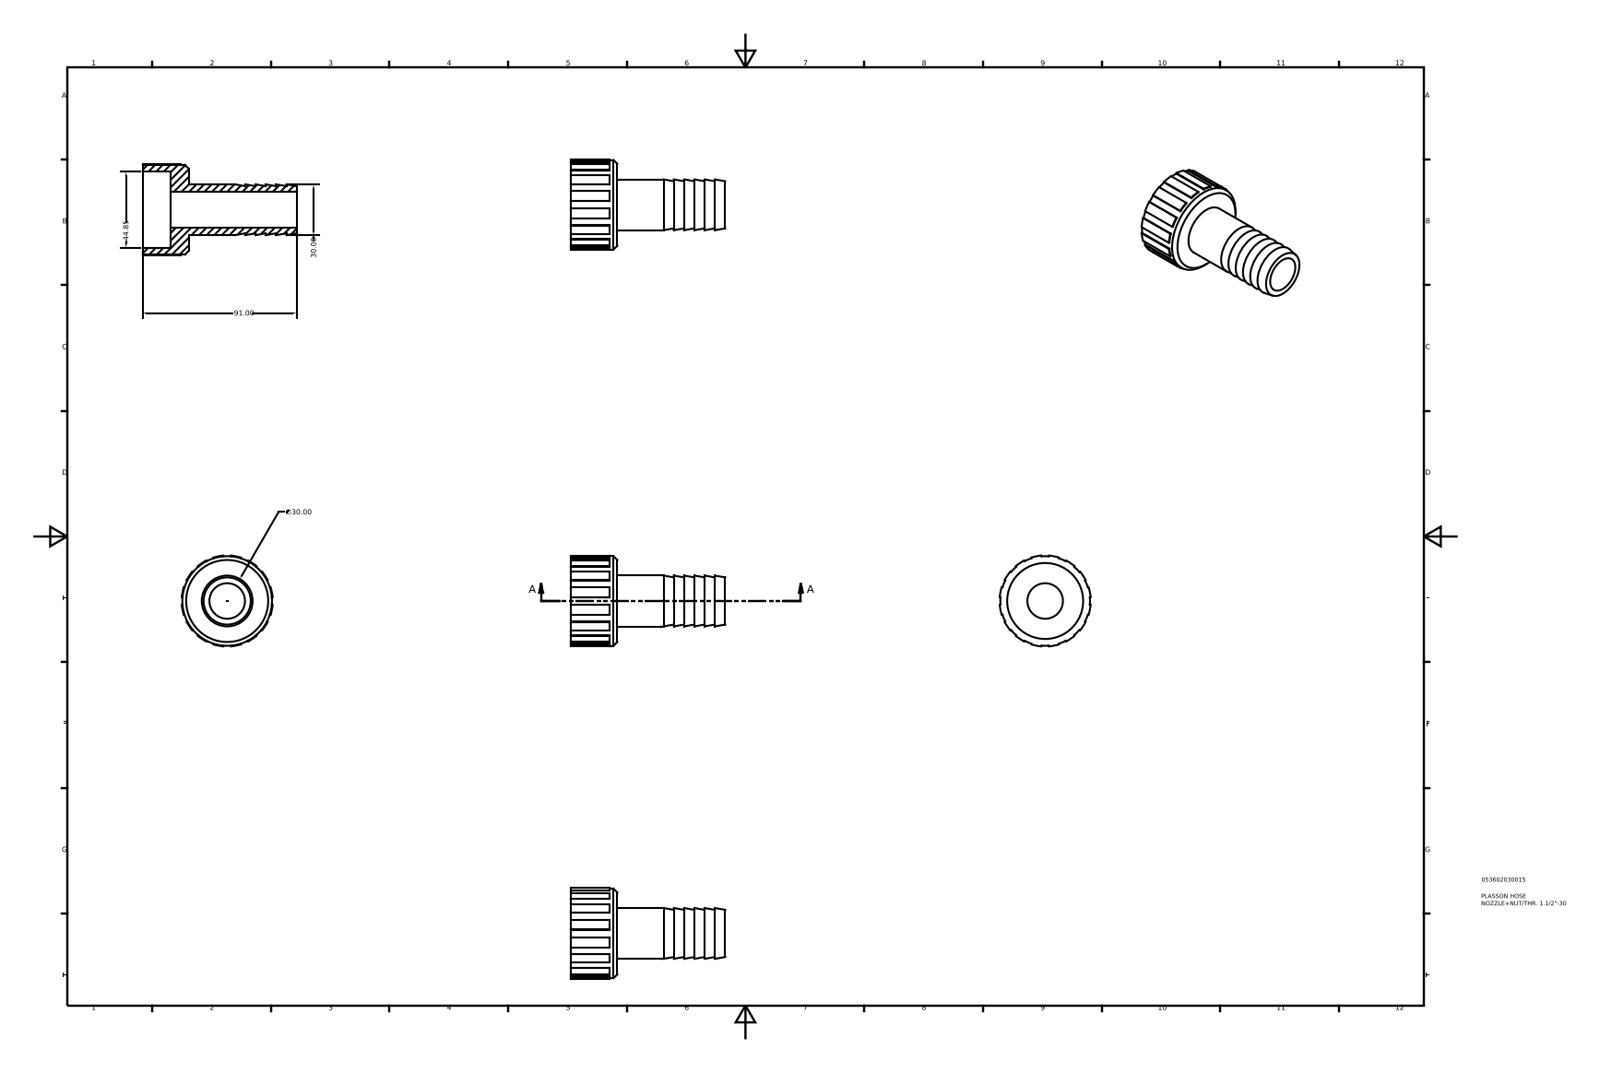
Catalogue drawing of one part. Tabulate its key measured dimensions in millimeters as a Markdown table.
| quantity | value |
| --- | --- |
| part name | 053602030015 |
| STEP written by | Autodesk Inventor 2015 (AUTOMOTIVE_DESIGN) |
| units | millimeters |
| bodies | 1 solid, 84 faces (57 planar, 20 cylindrical, 7 other) |
| overall size | 91 × 53.63 × 53.63 |
| volume | 52 136 mm³ |
| surface area | 22 021 mm² |
| round holes (diameter × count) | 21 × 1, 44.84 × 1 |
| round bosses / shafts (diameter × count) | 52.92 × 1, 30 × 1 |
| partial cylindrical surfaces (radius × count) | 26.91 × 1 |
| main face-to-face distances | 10.92, 16.38, 27.3, 12.13, 18.2, 6.07, 91, 74.62, 63.7, 6.06 |
